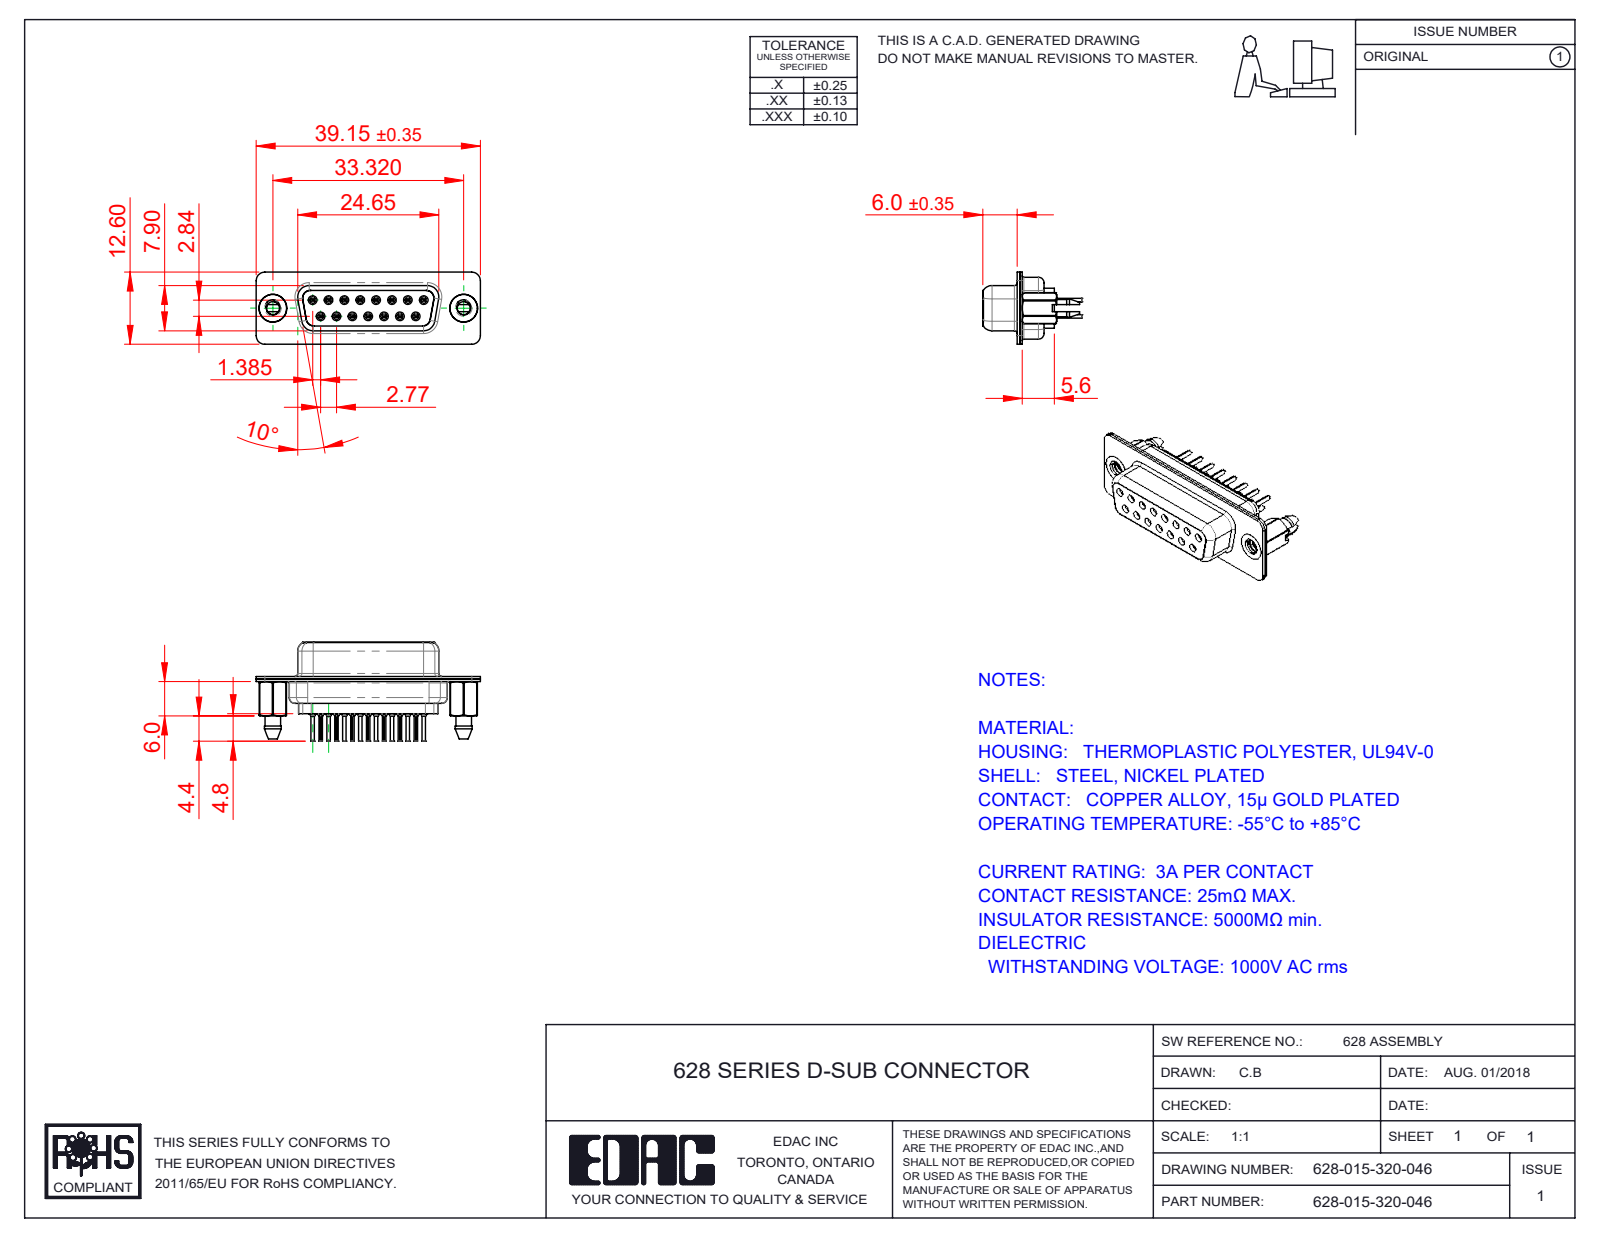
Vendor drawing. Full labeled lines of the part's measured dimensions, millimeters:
Part name (STEP PRODUCT): 628 Housing_15 LP; 628 Contact Row 2_20L; 628 Shell Front_15 Contacts; 628 Shell Rear_15 Contacts (+3 more)
STEP written by: SolidWorks 2020 (CONFIG_CONTROL_DESIGN)
Units: millimetres
Bodies: 20 solids, 2258 faces (564 planar, 664 cylindrical, 1030 other)
Overall size (bounding box): 39.15 × 17.3 × 12.6
Volume: 2 658 mm³ · Surface area: 6 617 mm²
Round holes (diameter × count): ⌀0.2 ×15, ⌀0.8 ×15, ⌀0.9 ×15, ⌀1.1 ×15, ⌀1.6 ×15, ⌀1.7 ×8, ⌀2.26 ×2, ⌀4 ×2, ⌀4.05 ×2, ⌀4.85 ×2
Round bosses / shafts (diameter × count): ⌀2 ×15, ⌀1.5 ×15, ⌀1.2 ×15, ⌀0.6 ×15, ⌀4.95 ×2, ⌀4.8 ×2
Partial cylindrical surfaces — rounded edges, fillets, slot ends (radius × count): R0.1 ×30, R1.5 ×20, R0.28 ×15, R2 ×12, R1.35 ×8, R1.6 ×6, R0.25 ×4, R0.5 ×4
Main face-to-face distances: 0.45, 0.4, 0.9, 6.6, 1.9, 8.5, 1.4, 0.85, 7.05, 7.45
Hole centre spacings: 3.16, 2.77, 5.54, 8.31, 11.08, 5.03, 5.04, 7.48
